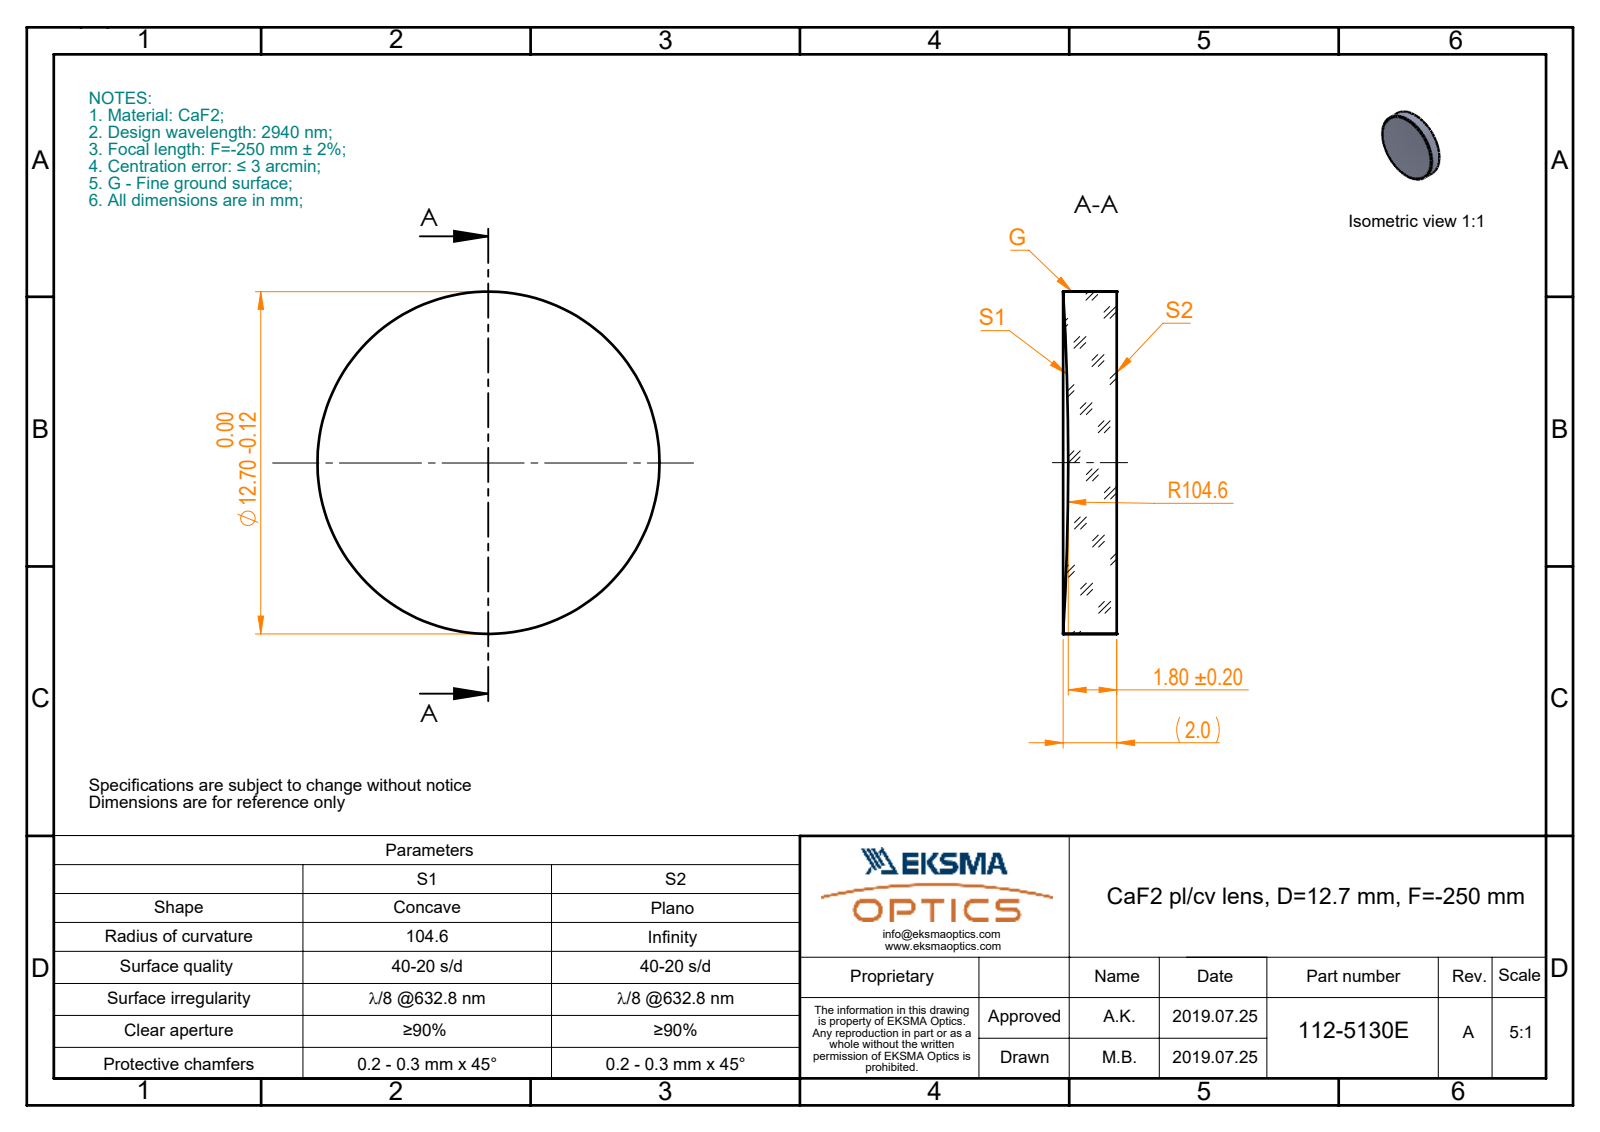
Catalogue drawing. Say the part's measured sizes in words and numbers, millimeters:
The part is named "112-5130E CaF2 pl-cv 12.7 F-250". Its 3-D file was written by "SolidWorks 2017 (CONFIG_CONTROL_DESIGN)". It is 1 solid with 5 faces: 1 planar, 2 cylindrical and 2 other. Overall it measures 50.8 by 50.8 by 5.6 millimeters. Its volume is 8 703 cubic millimeters and its surface area 4 968 square millimeters. Round bosses or shafts: 1 of diameter 50.8.
